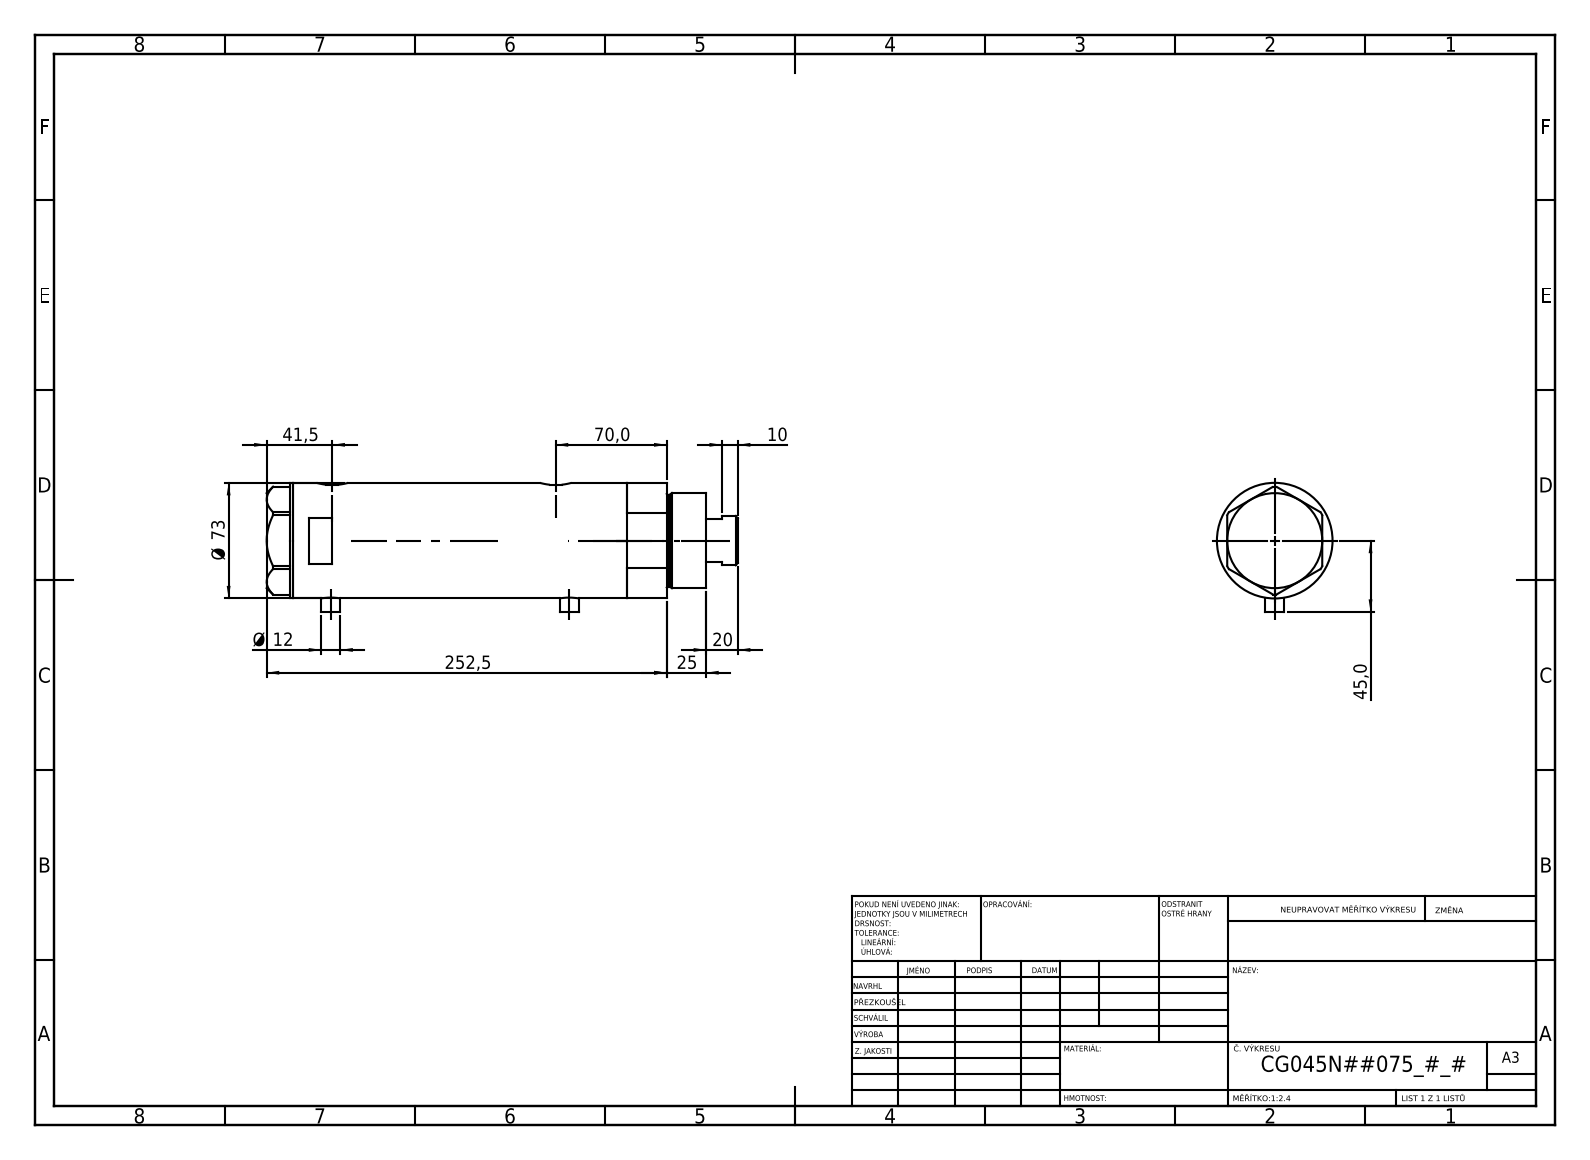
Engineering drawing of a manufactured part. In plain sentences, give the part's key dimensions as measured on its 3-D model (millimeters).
The part is named "V270CG_MIDDLE; V270CG_BACK; V270CG_VC; V270CG_FRONT". Its 3-D file was written by "SolidWorks 2019 (CONFIG_CONTROL_DESIGN)". It is 4 solids with 120 faces: 49 planar, 51 cylindrical and 20 other. Overall it measures 297.5 by 81.5 by 73 millimeters. Its volume is 1 055 000 cubic millimeters and its surface area 170 973 square millimeters. Round holes: 2 of diameter 12.5, 2 of diameter 13.16, 1 of diameter 10.5, 1 of diameter 32, 1 of diameter 33.5, 1 of diameter 45, 1 of diameter 48, 1 of diameter 64. Round bosses or shafts: 2 of diameter 12, 1 of diameter 73, 1 of diameter 60, 1 of diameter 58, 1 of diameter 31. Partial cylindrical surfaces (rounded edges, fillets, slot ends): 2 of radius 10. The main face-to-face distances are 166, 26, 140, 16.5, 42.5, 182.5, 2, 261, 277.5, 235. The hole center spacings are 1, 8.5, 141, 142, 149.5, 150.5.
